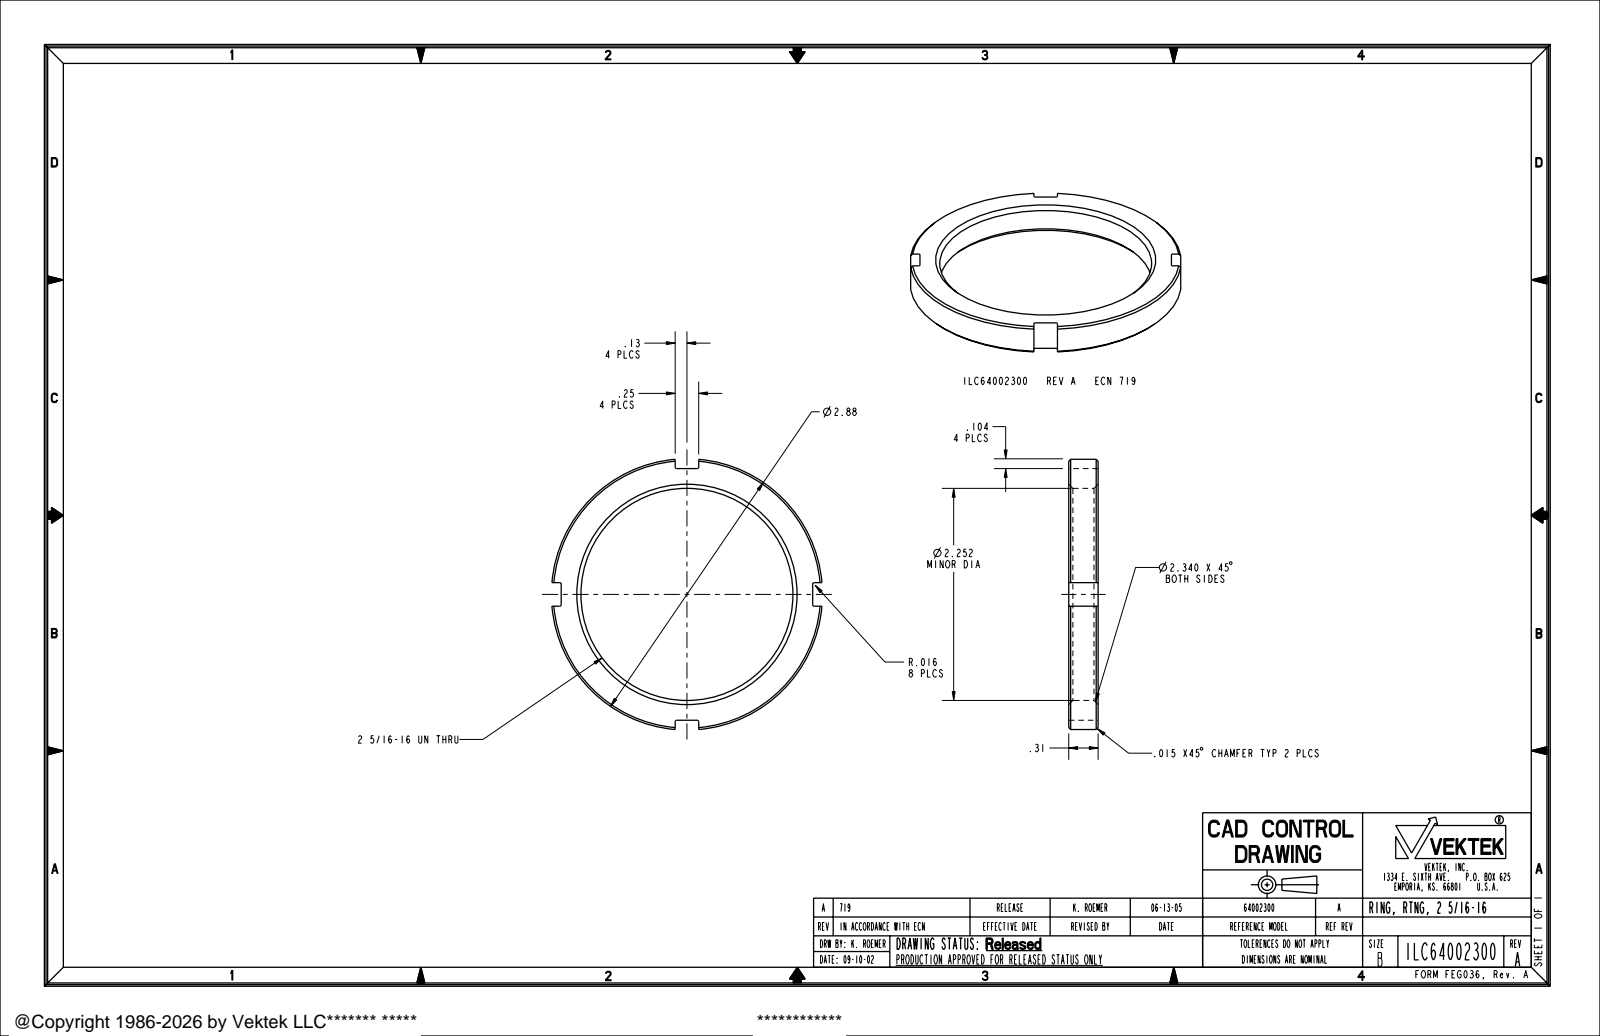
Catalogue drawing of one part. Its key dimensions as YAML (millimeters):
part_name: "ILC64002300"
step_written_by: "PRO/ENGINEER BY PARAMETRIC TECHNOLOGY CORPORATION, 2004290 (AUTOMOTIVE_DESIGN_CC2)"
units: millimeters
bodies: {solids: 1, faces: 40, planar: 14, cylindrical: 14, other: 12}
overall_size: [73.2, 73.2, 7.9]
volume: 12100
surface_area: 6168
round_holes:
  - {diameter: 57.2, count: 1}
round_bosses_or_shafts:
  - {diameter: 73.2, count: 1}
partial_cylinders:
  - {radius: 0.4, count: 8}
face_to_face_distances: [7.9, 30.8, 37.1, 67.9, 6.4]
